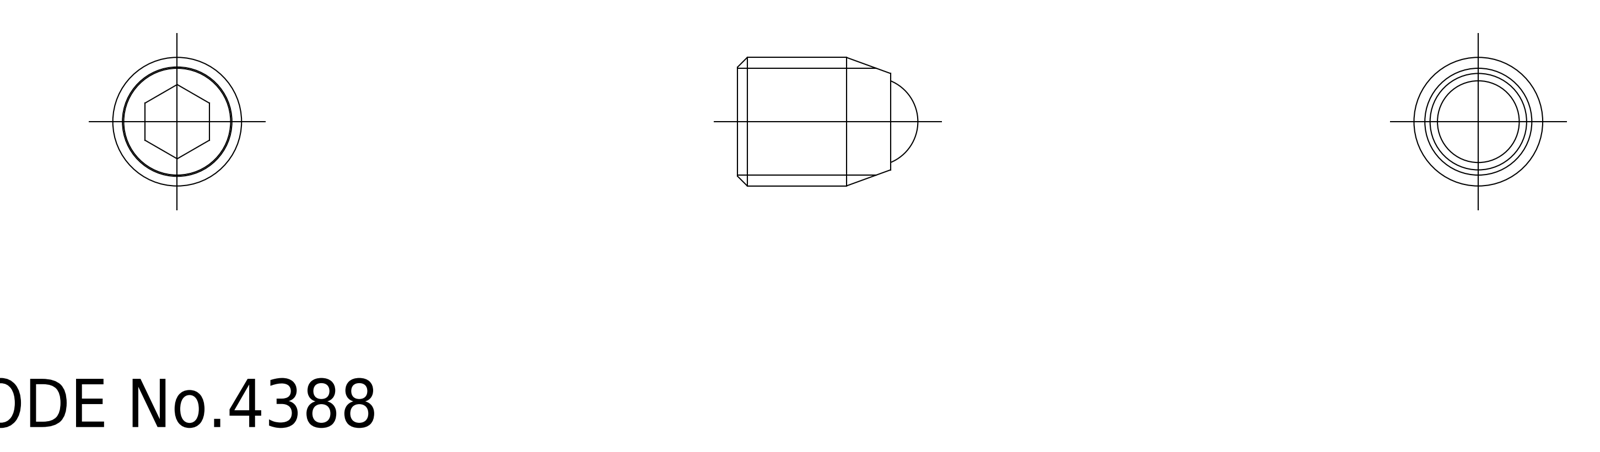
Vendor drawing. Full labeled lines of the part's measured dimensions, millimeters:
Part name (STEP PRODUCT): ball; SCS_M8_10_R_17623_36
STEP written by: CADfix (AUTOMOTIVE_DESIGN)
Units: millimetres
Bodies: 2 solids, 20 faces (0 planar, 0 cylindrical, 20 other)
Overall size (bounding box): 11.2 × 8 × 8
Volume: 356 mm³ · Surface area: 540 mm²
